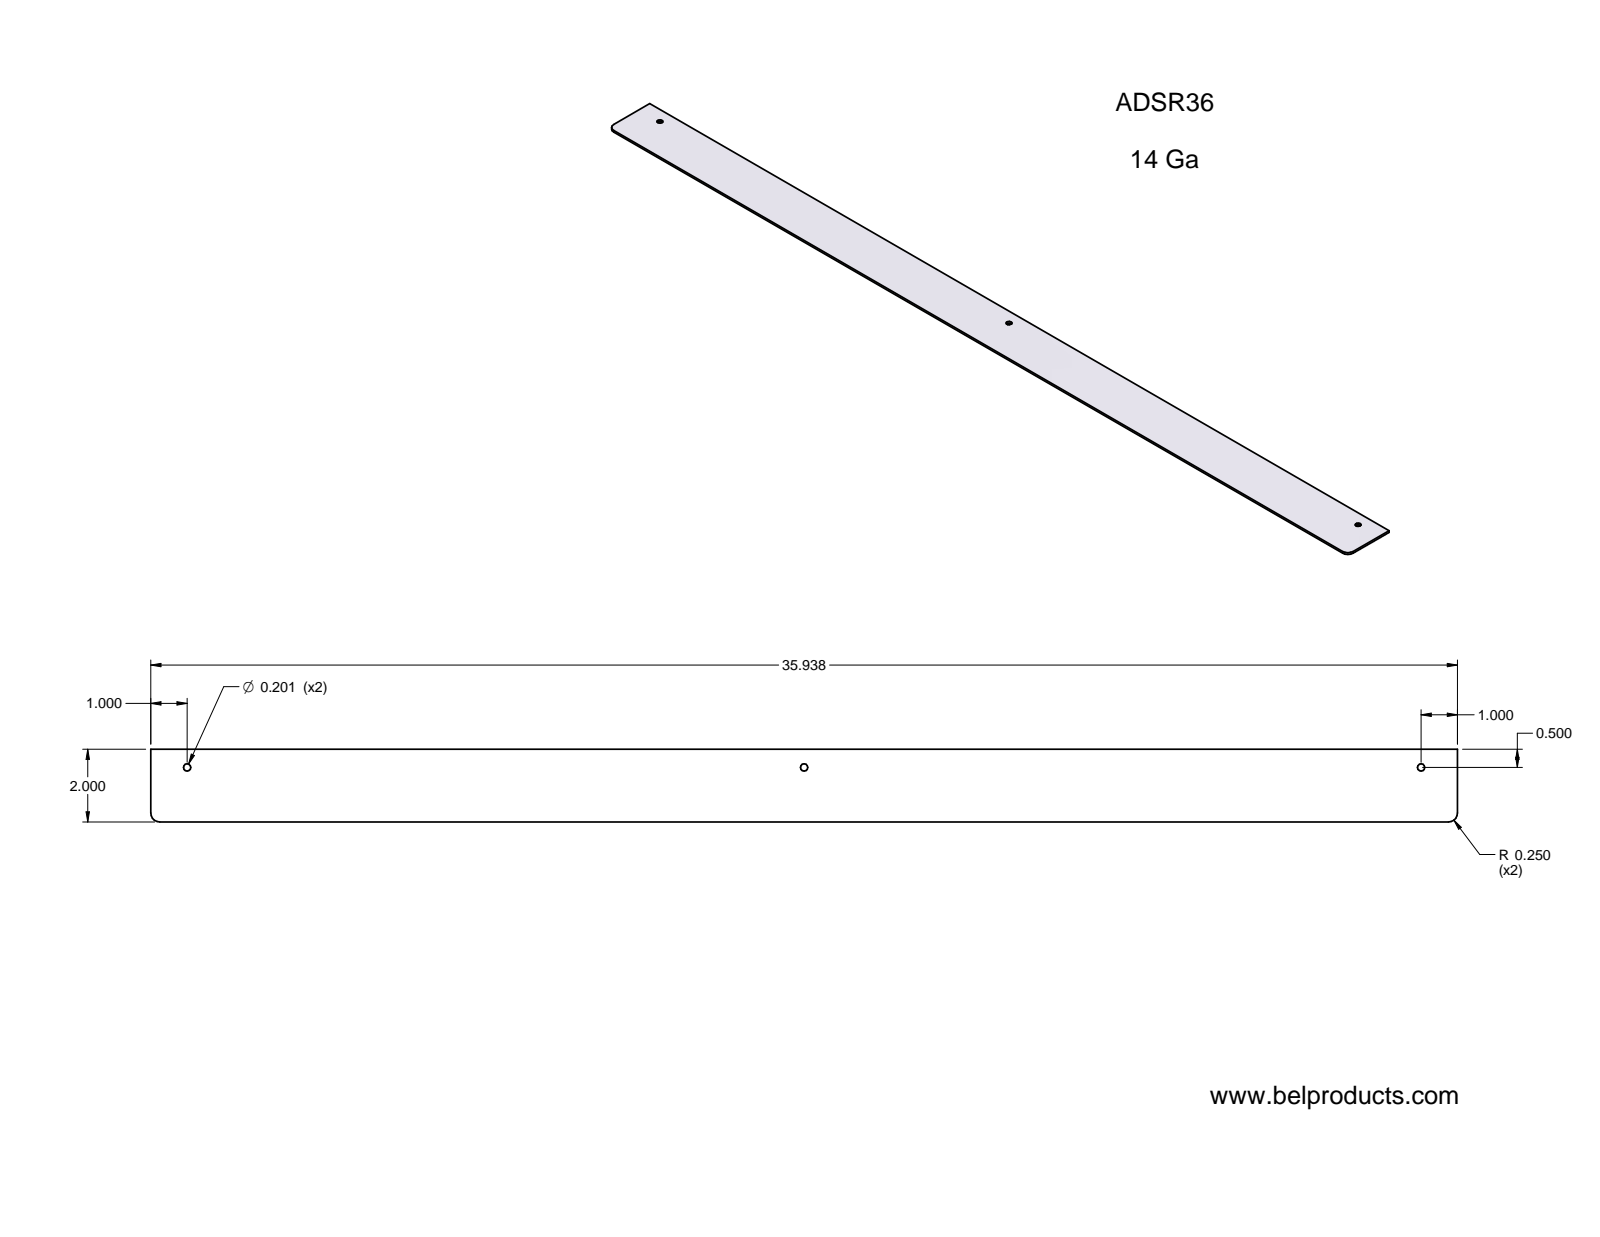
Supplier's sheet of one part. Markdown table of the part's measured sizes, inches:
| quantity | value |
| --- | --- |
| STEP written by | Unknown (AUTOMOTIVE_DESIGN) |
| units | inches |
| bodies | 1 solid, 11 faces (6 planar, 5 cylindrical, 0 other) |
| overall size | 35.937 × 2 × 0.075 |
| volume | 5.382 in³ |
| surface area | 149.3 in² |
| round holes (diameter × count) | 0.201 × 3 |
| partial cylindrical surfaces (radius × count) | 0.25 × 2 |
| main face-to-face distances | 0.075, 2, 35.938 |
| hole center spacings | 16.969, 33.938 |
